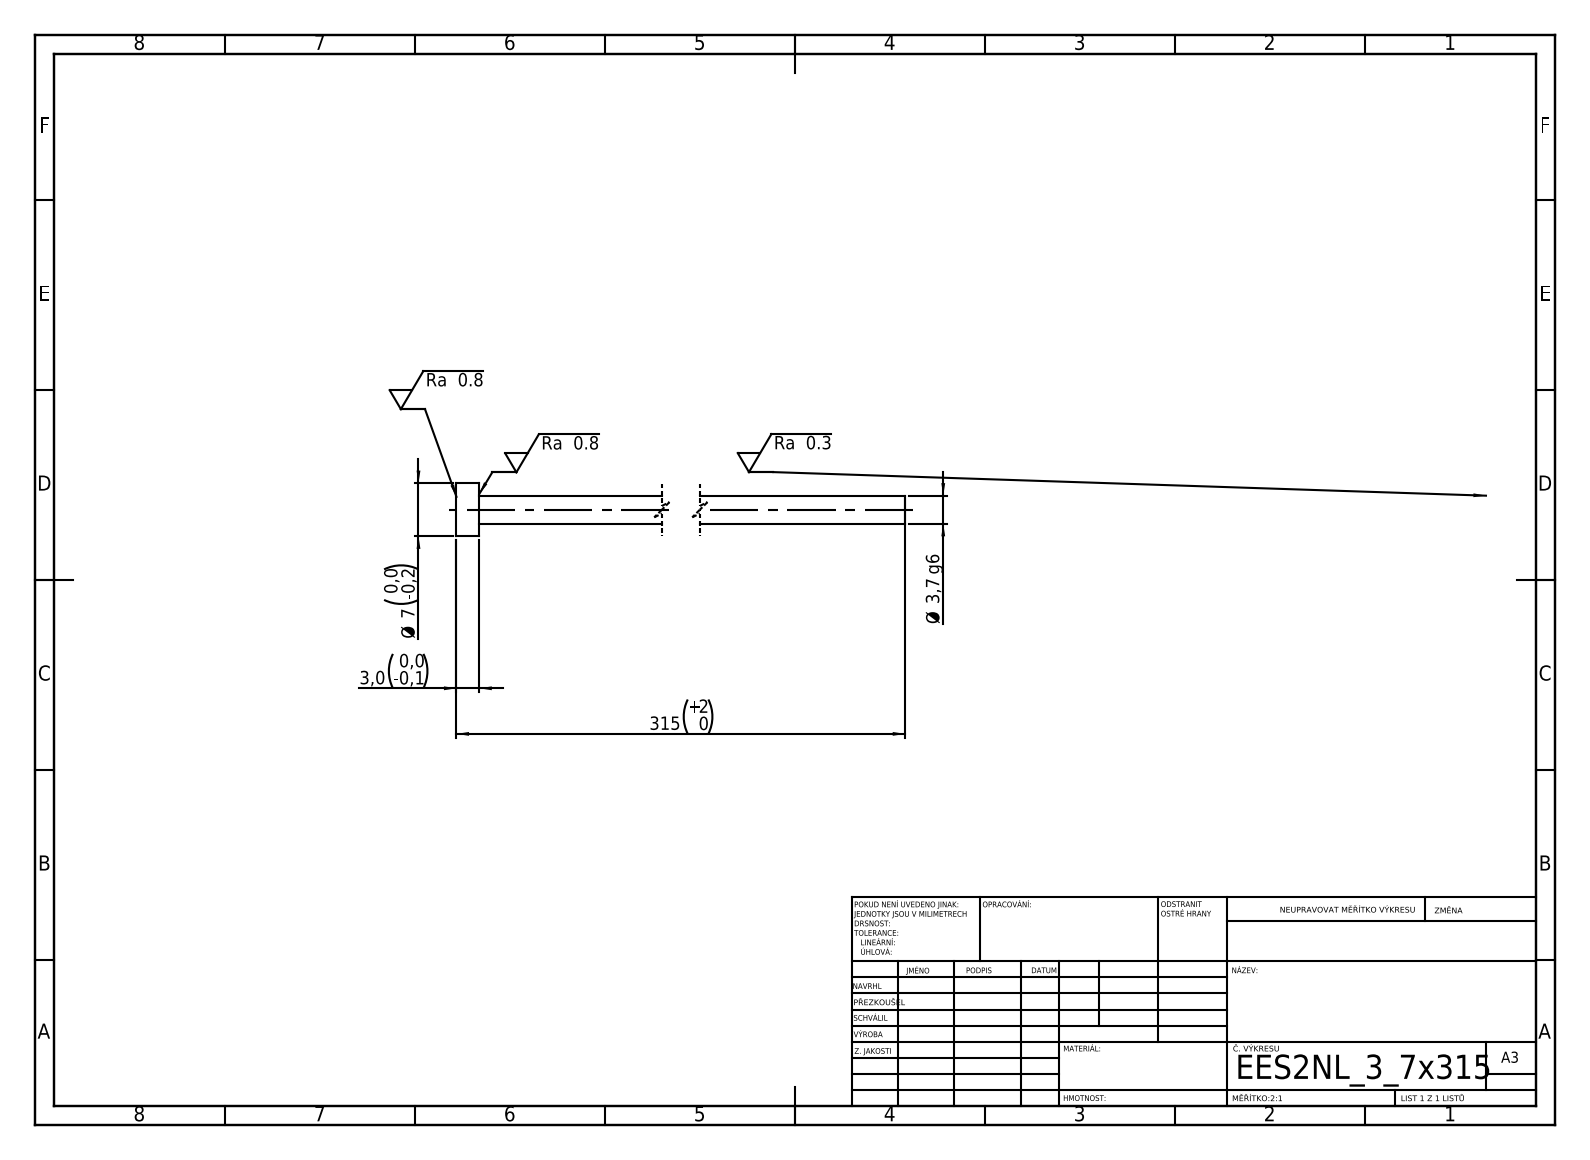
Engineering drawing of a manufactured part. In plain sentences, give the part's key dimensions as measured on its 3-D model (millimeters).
Its 3-D file was written by "SolidWorks 2019 (CONFIG_CONTROL_DESIGN)". It is 1 solid with 7 faces: 3 planar, 4 cylindrical and 0 other. Overall it measures 315 by 7 by 7 millimeters. Its volume is 3 470 cubic millimeters and its surface area 3 770 square millimeters. Round bosses or shafts: 1 of diameter 7, 1 of diameter 3.7. The main face-to-face distances are 3, 315, 312.
